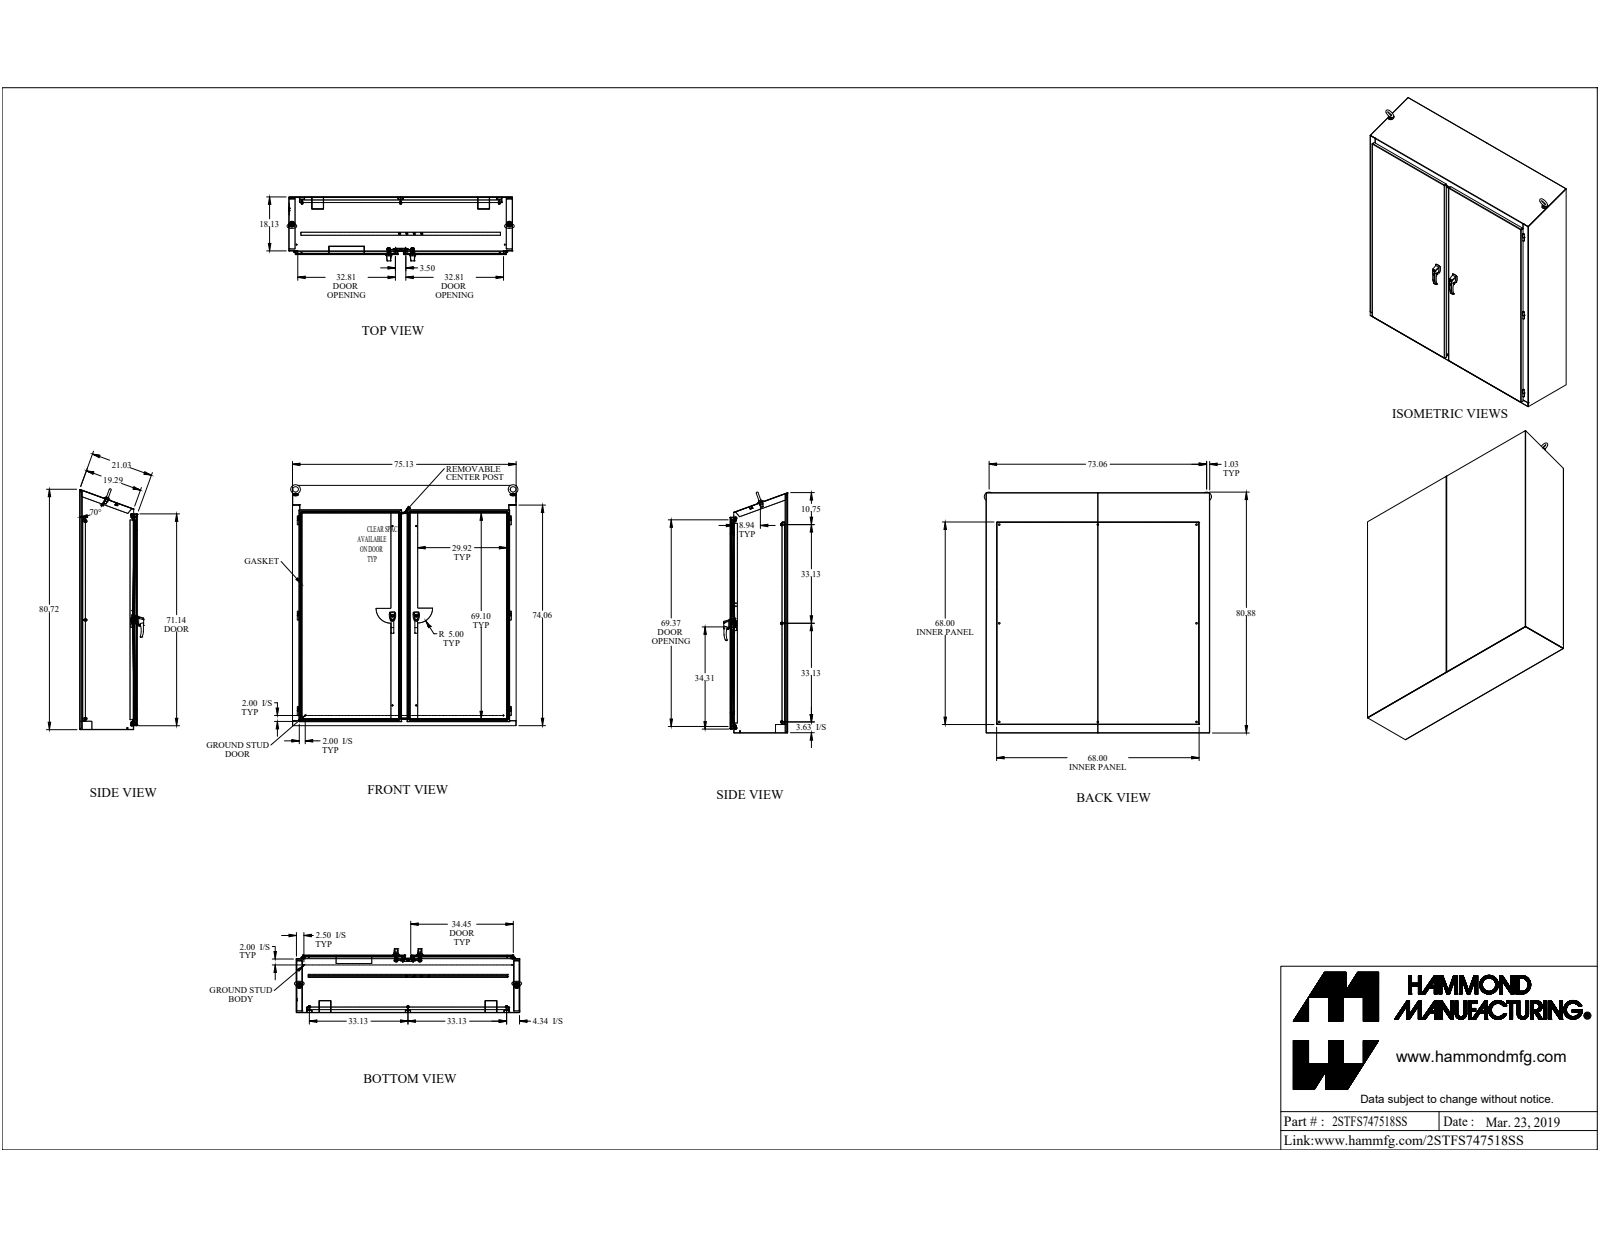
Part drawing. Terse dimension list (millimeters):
name: 2STFS747518SS
written by: SolidWorks 2019 (CONFIG_CONTROL_DESIGN)
unit: mm
bodies: 146 solids, 2404 faces (1417 planar, 729 cylindrical, 258 other)
size: 2054.5 × 1938.2 × 545.9
volume: 42 880 000 mm³; area: 33 610 000 mm²
holes: 8× ⌀7.8, 8× ⌀8.9, 8× ⌀14.3, 7× ⌀6.4, 6× ⌀7.1, 6× ⌀8, 6× ⌀11.3, 4× ⌀5, 4× ⌀6.5, 4× ⌀7.1, 4× ⌀9.9, 4× ⌀10.5
bosses: 12× ⌀25.4, 8× ⌀16.5, 8× ⌀9.5, 8× ⌀8.4, 4× ⌀19.1, 4× ⌀16, 4× ⌀15.9, 4× ⌀11.2
rounds: 47× R3.2, 33× R12.7, 32× R0.5, 30× R1.2, 30× R3.6, 20× R1.5, 16× R6.4, 12× R0.8
face distances: 2.4, 2.4, 487.3, 489.7, 489.7, 492.2, 3.2, 443.7, 441.3, 46
hole spacings: 1855.7, 202.8, 1881.4, 1682.8, 28.6, 32.7, 189.1, 204.8
